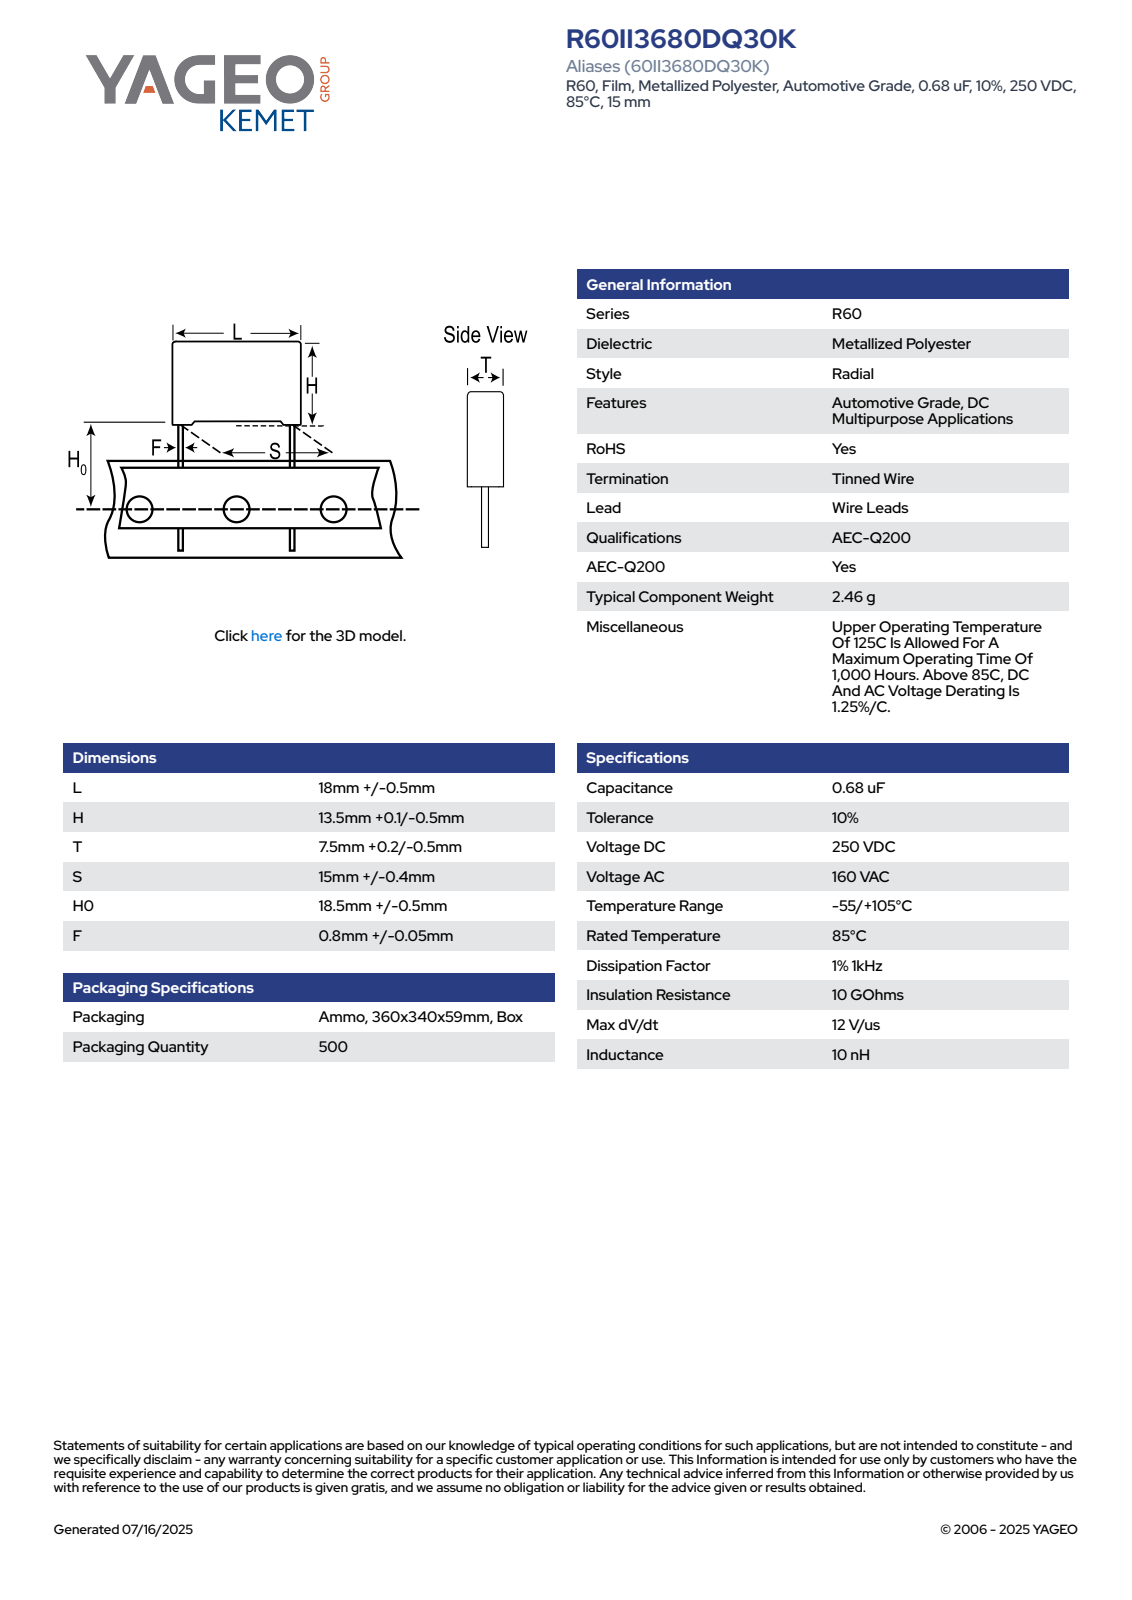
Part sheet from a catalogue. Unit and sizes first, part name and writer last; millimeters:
Units: millimetres
Overall size (bounding box): 32.6 × 18.5 × 7.71
Round bosses / shafts (diameter × count): ⌀0.85 ×2
Partial cylindrical surfaces — rounded edges, fillets, slot ends (radius × count): R0.5 ×4
Main face-to-face distances: 7.7, 12.85, 18.5, 0.62, 0.75, 13.6, 7.08, 0.47, 13.13, 17.88
Volume: 1 867 mm³ · Surface area: 1 132 mm²
Bodies: 4 solids, 85 faces (77 planar, 8 cylindrical, 0 other)
Part name (STEP PRODUCT): CFR_RB2_18X13.5X7.5_L18.5H13.6T7.7S15H019F0.85
STEP written by: SolidWorks 2020 (AUTOMOTIVE_DESIGN)
